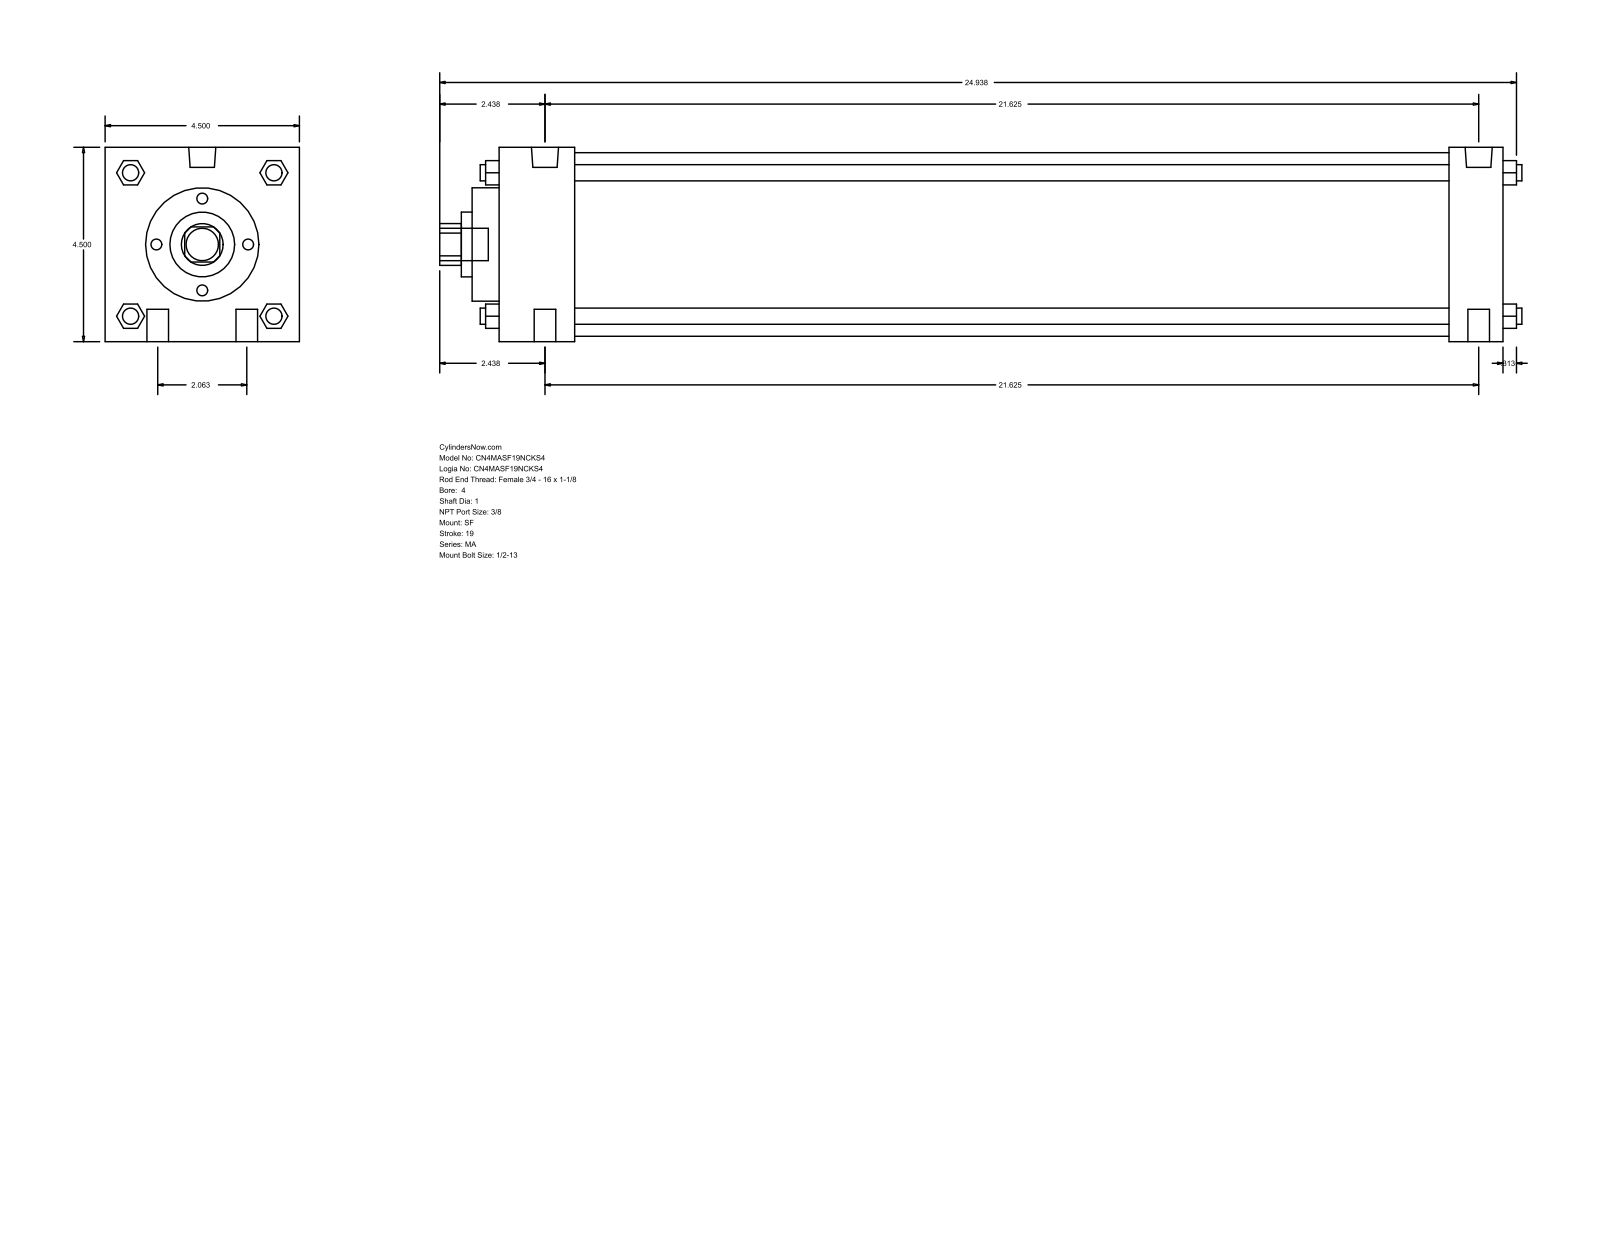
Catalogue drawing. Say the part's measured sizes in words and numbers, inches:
The part is named "MA_SF__0400_1". Its 3-D file was written by "GSSL Pune (CONFIG_CONTROL_DESIGN)". It is 0 solids with 126 faces: 95 planar, 31 cylindrical and 0 other. Overall it measures 25.063 by 4.5 by 4.5 inches. Round holes: 1 of diameter 1, 1 of diameter 1.5, 1 of diameter 2.625, 1 of diameter 4.25. Round bosses or shafts: 4 of diameter 0.5, 4 of diameter 0.375, 2 of diameter 0.627, 2 of diameter 0.437, 1 of diameter 0.75. Partial cylindrical surfaces (rounded edges, fillets, slot ends): 1 of radius 0.484. The main face-to-face distances are 4.5, 23.25, 22, 1.25, 1.75, 20.25, 21.5, 0.625, 2.375, 22.625.
